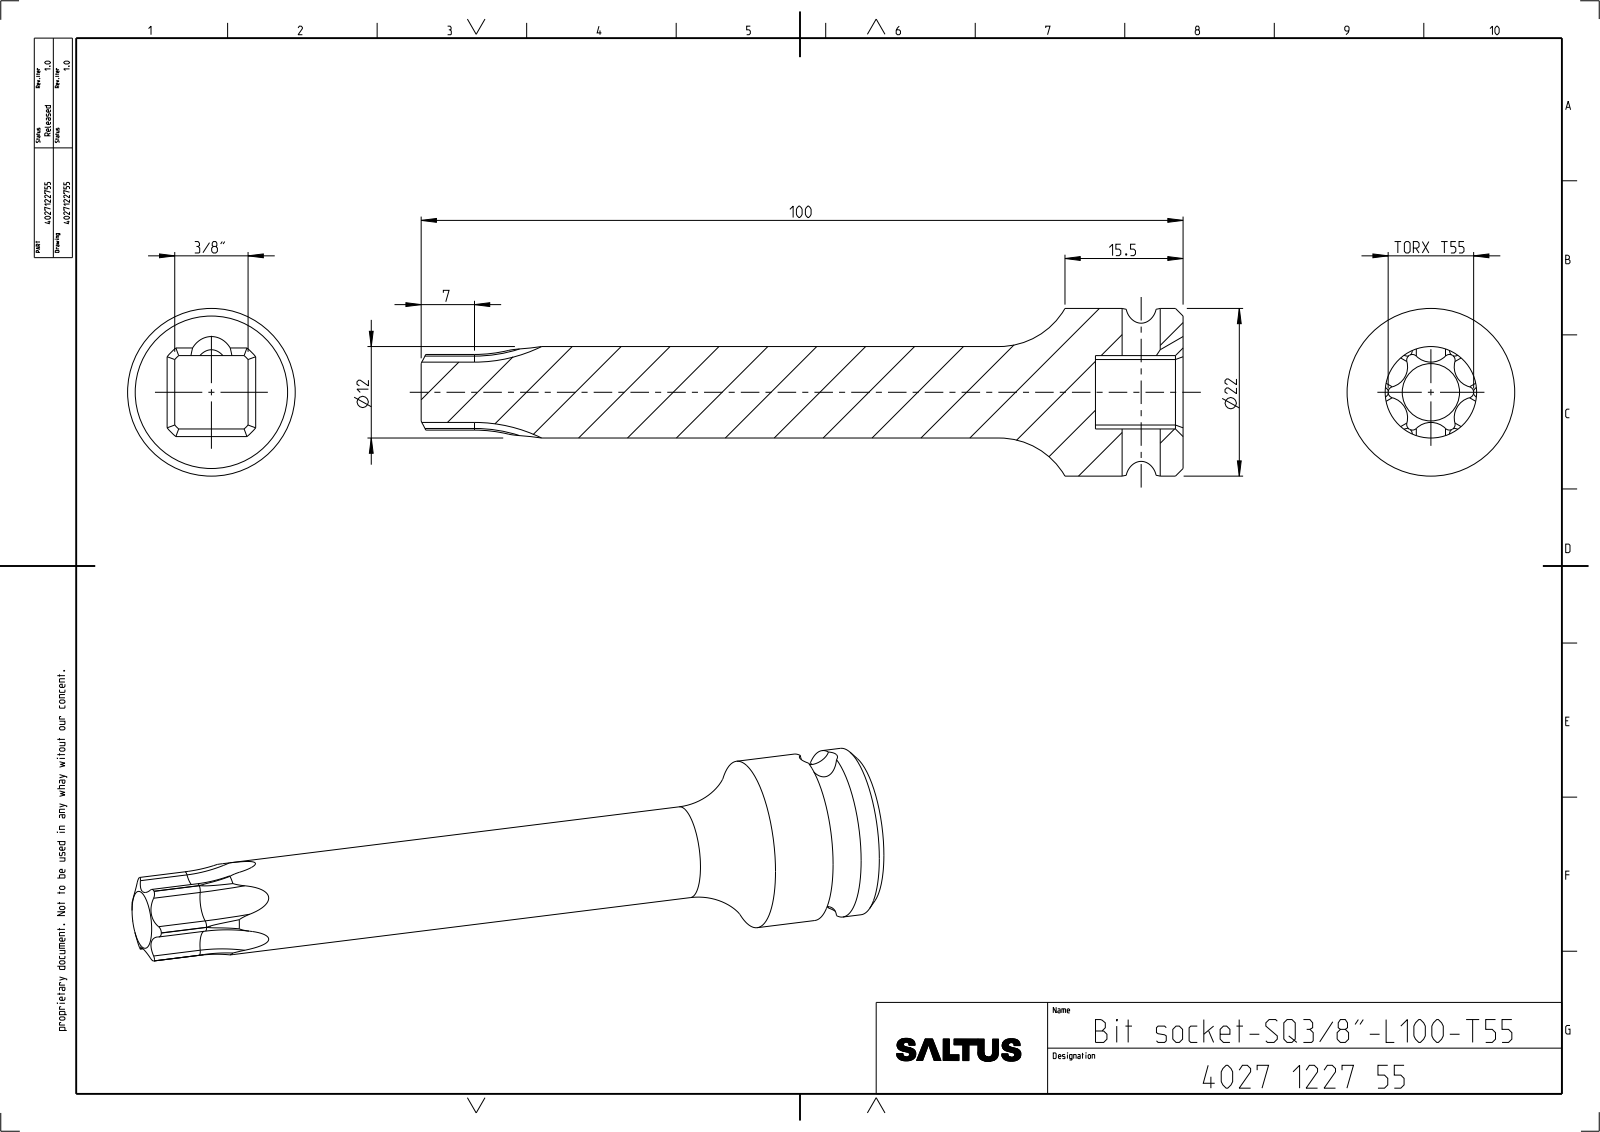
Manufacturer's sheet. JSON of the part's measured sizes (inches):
{"part_name": "4027122755", "step_written_by": "CREO PARAMETRIC BY PTC INC, 2022414 (CONFIG_CONTROL_DESIGN)", "units": "inches", "bodies": {"solids": 1, "faces": 87, "planar": 12, "cylindrical": 39, "other": 36}, "overall_size": [3.937, 0.866, 0.866], "volume_in3": 0.845, "surface_area_in2": 8.368, "round_holes": [[0.197, 1]], "round_bosses_or_shafts": [[0.866, 1], [0.472, 1]], "partial_cylinders_radius": [[0.029, 12], [0.107, 6], [0.118, 1], [0.221, 1], [0.254, 1]], "face_to_face_distances": [0.379, 0.453, 3.937, 3.484]}
